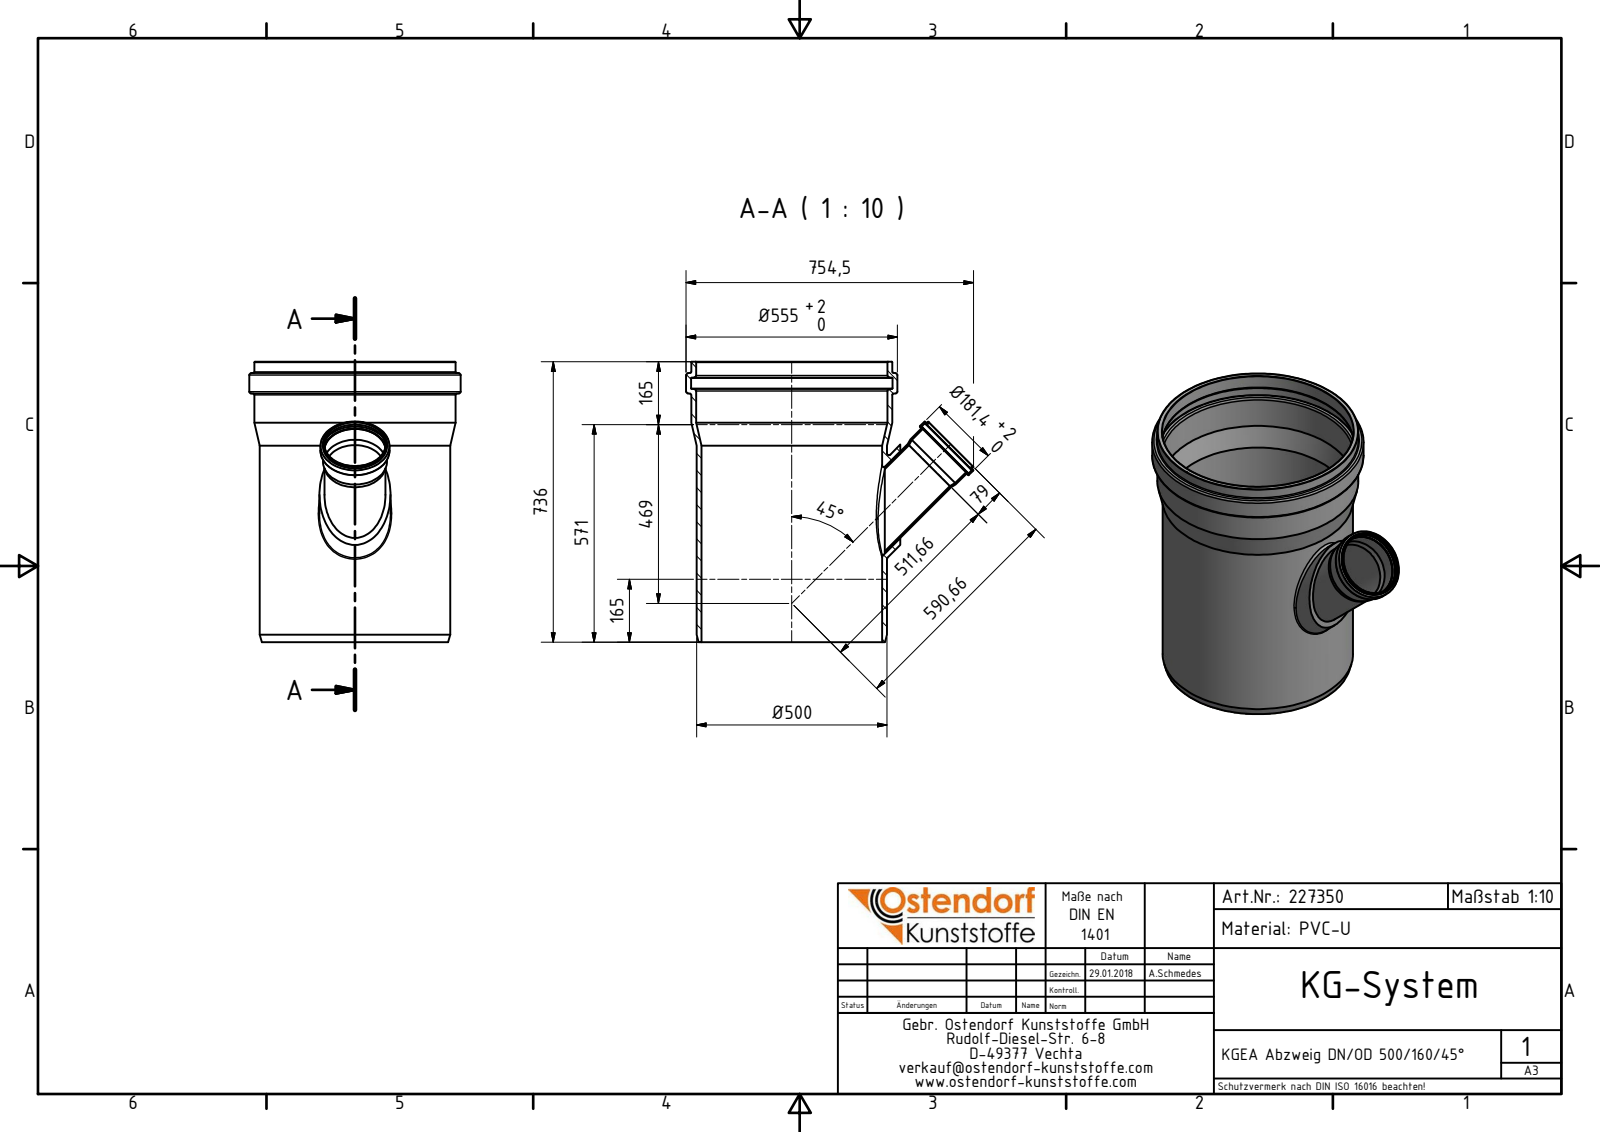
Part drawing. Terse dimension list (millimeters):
name: 227350 KGEA Abzweig DN_OD 500_160_45° Abzweig; 227350 KGEA Abzweig DN_OD 500_160_45°
written by: Autodesk Inventor 2016 (AUTOMOTIVE_DESIGN)
unit: mm
bodies: 2 solids, 60 faces (6 planar, 19 cylindrical, 35 other)
size: 754.5 × 736 × 555
volume: 15 870 000 mm³; area: 2 669 000 mm²
holes: 1× ⌀152.3, 1× ⌀160.3, 1× ⌀160.7, 1× ⌀161.1, 1× ⌀174.4, 1× ⌀474, 1× ⌀502, 1× ⌀529
bosses: 1× ⌀555, 1× ⌀528, 1× ⌀500, 1× ⌀186.3, 1× ⌀181.4, 1× ⌀168.1, 1× ⌀167.7, 1× ⌀160.3
face distances: 736, 40.47, 23.61
